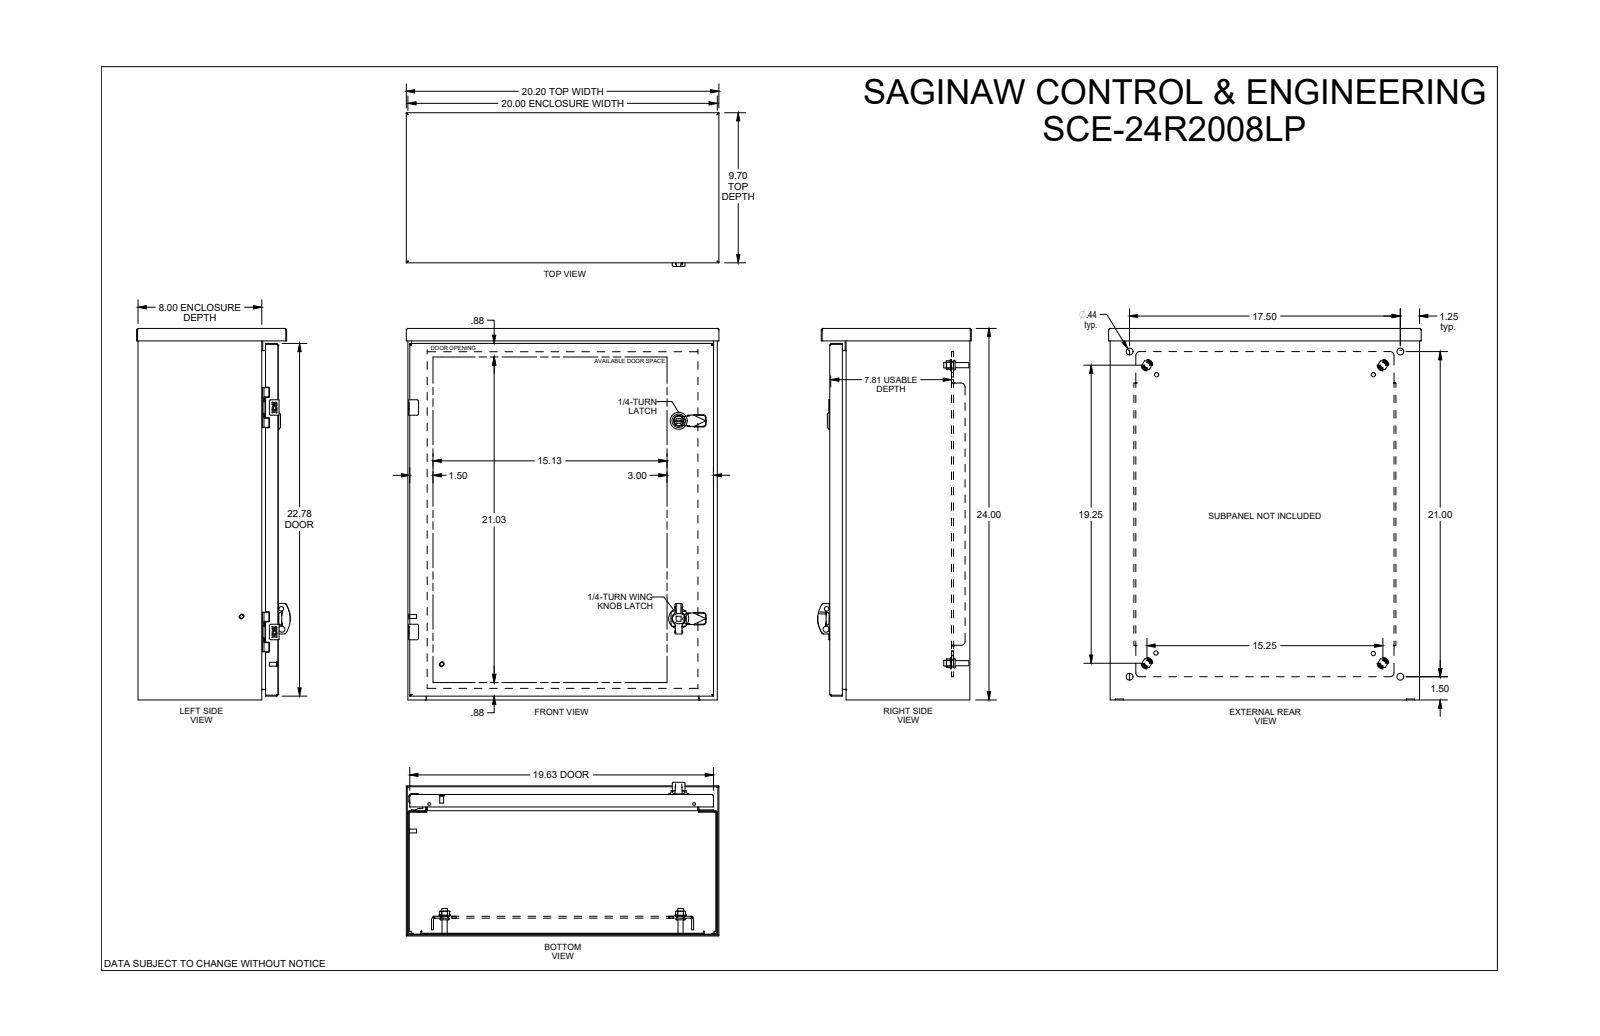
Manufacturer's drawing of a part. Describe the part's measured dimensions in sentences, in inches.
The part is named "SCE-24R2008LP". Its 3-D file was written by "SolidWorks 2019 (CONFIG_CONTROL_DESIGN)". It is 0 solids with 2365 faces: 1132 planar, 799 cylindrical and 434 other. Overall it measures 24 by 20.2 by 9.927 inches. Round holes: 4 of diameter 0.172, 4 of diameter 0.205, 4 of diameter 0.244, 4 of diameter 0.266, 4 of diameter 0.281, 4 of diameter 0.367, 4 of diameter 0.375, 4 of diameter 0.438, 4 of diameter 0.5, 2 of diameter 0.04, 2 of diameter 0.156, 2 of diameter 0.188. Round bosses or shafts: 6 of diameter 0.17, 4 of diameter 0.366, 4 of diameter 0.332, 4 of diameter 0.25, 4 of diameter 0.24, 3 of diameter 0.196, 2 of diameter 0.866, 2 of diameter 0.802. Partial cylindrical surfaces (rounded edges, fillets, slot ends): 72 of radius 0.015, 60 of radius 0.012, 26 of radius 0.01, 24 of radius 0.02, 21 of radius 0.112, 19 of radius 0.052, 15 of radius 0.03, 12 of radius 0.031. The main face-to-face distances are 0.06, 0.06, 8.933, 8.993, 9.053, 8.993, 0.125, 19.94, 1, 1.125. The hole center spacings are 14.5, 0.024, 0.493, 0.985, 16.398, 0.875, 2.296, 14.644.
